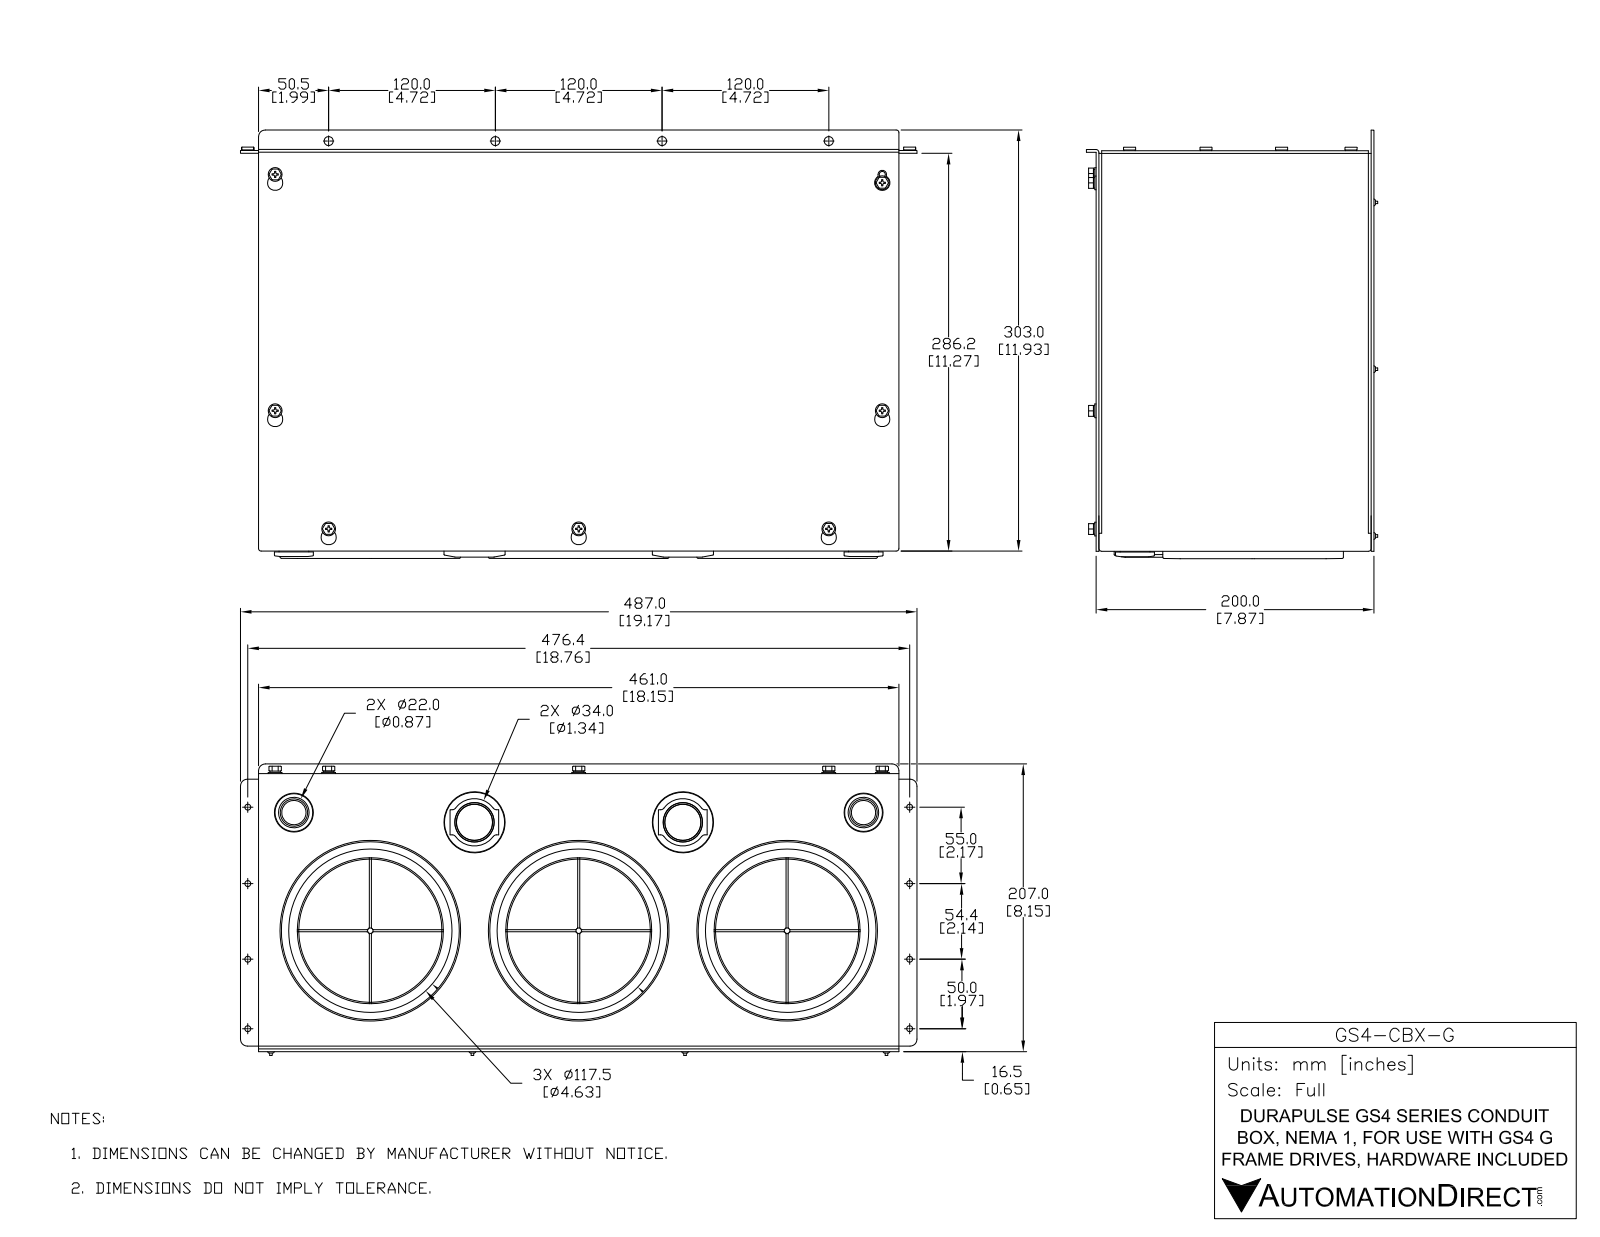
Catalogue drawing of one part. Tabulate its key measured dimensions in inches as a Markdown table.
| quantity | value |
| --- | --- |
| part name | GS4-CBX-G |
| STEP written by | SolidWorks 2015 (AUTOMOTIVE_DESIGN) |
| units | inches |
| bodies | 0 solids, 607 faces (206 planar, 291 cylindrical, 110 other) |
| overall size | 19.173 × 12.139 × 8.256 |
| round holes (diameter × count) | 0.165 × 8, 0.169 × 8, 0.256 × 8, 0.433 × 7, 0.106 × 6, 0.394 × 4, 0.157 × 3, 4.055 × 3, 0.142 × 2, 0.689 × 2 |
| round bosses / shafts (diameter × count) | 0.343 × 12, 0.315 × 8, 0.071 × 8, 0.39 × 7, 0.295 × 7, 0.189 × 4, 0.122 × 4, 5.118 × 3 |
| partial cylindrical surfaces (radius × count) | 0.039 × 44, 0.02 × 16, 0.079 × 8, 0.197 × 7 |
| main face-to-face distances | 0.079, 7.795, 7.717, 7.874, 18.071, 18.15, 17.992, 0.133, 0.068, 0.065 |
| hole center spacings | 4.724, 18.756, 0.236, 10.153, 14.173, 17.205, 18.626, 0.576 |
